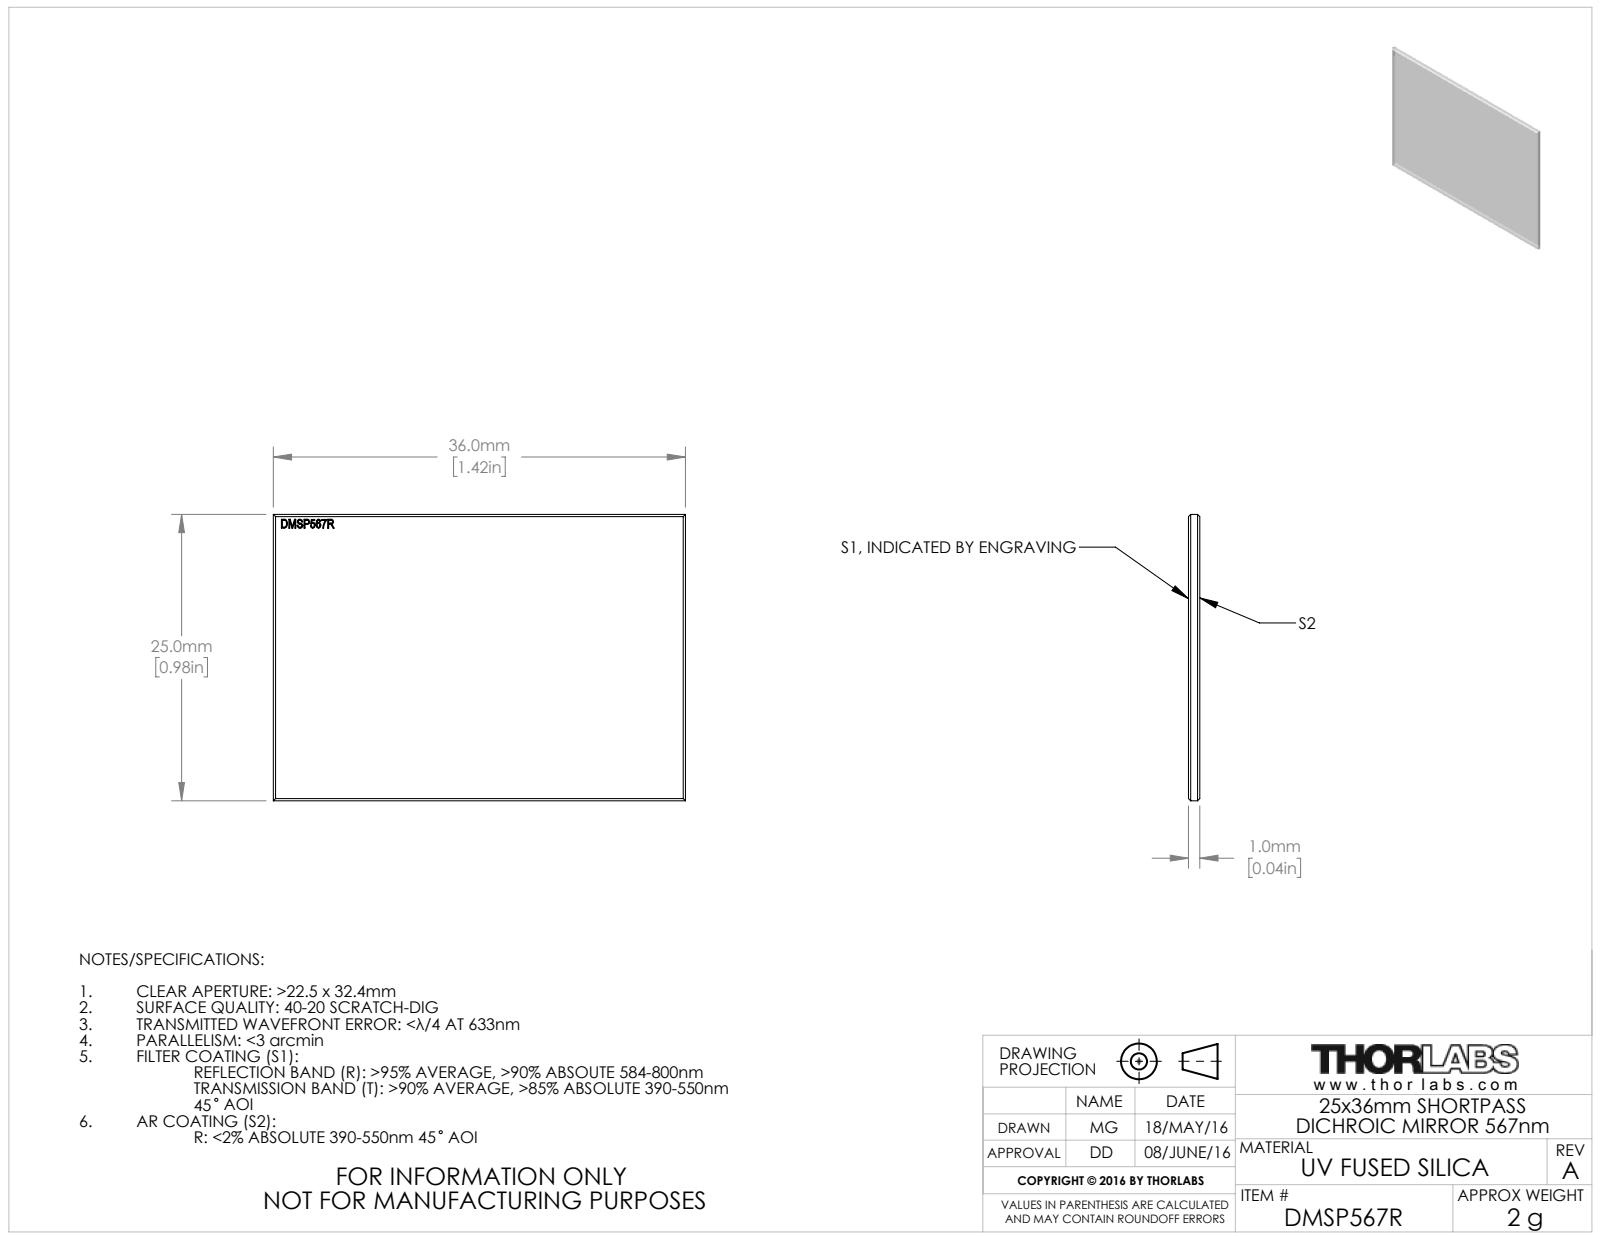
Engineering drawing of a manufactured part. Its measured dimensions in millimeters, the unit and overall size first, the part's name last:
Units: millimetres
Overall size (bounding box): 36 × 25 × 1
Main face-to-face distances: 1, 25, 18.1, 36, 25.88, 0.99, 0.72, 1.97, 0.8, 0.53
Volume: 895 mm³ · Surface area: 1 894 mm²
Bodies: 1 solid, 138 faces (80 planar, 0 cylindrical, 58 other)
Part name (STEP PRODUCT): TTN045180-E0W
STEP written by: SolidWorks 2016 (CONFIG_CONTROL_DESIGN)
